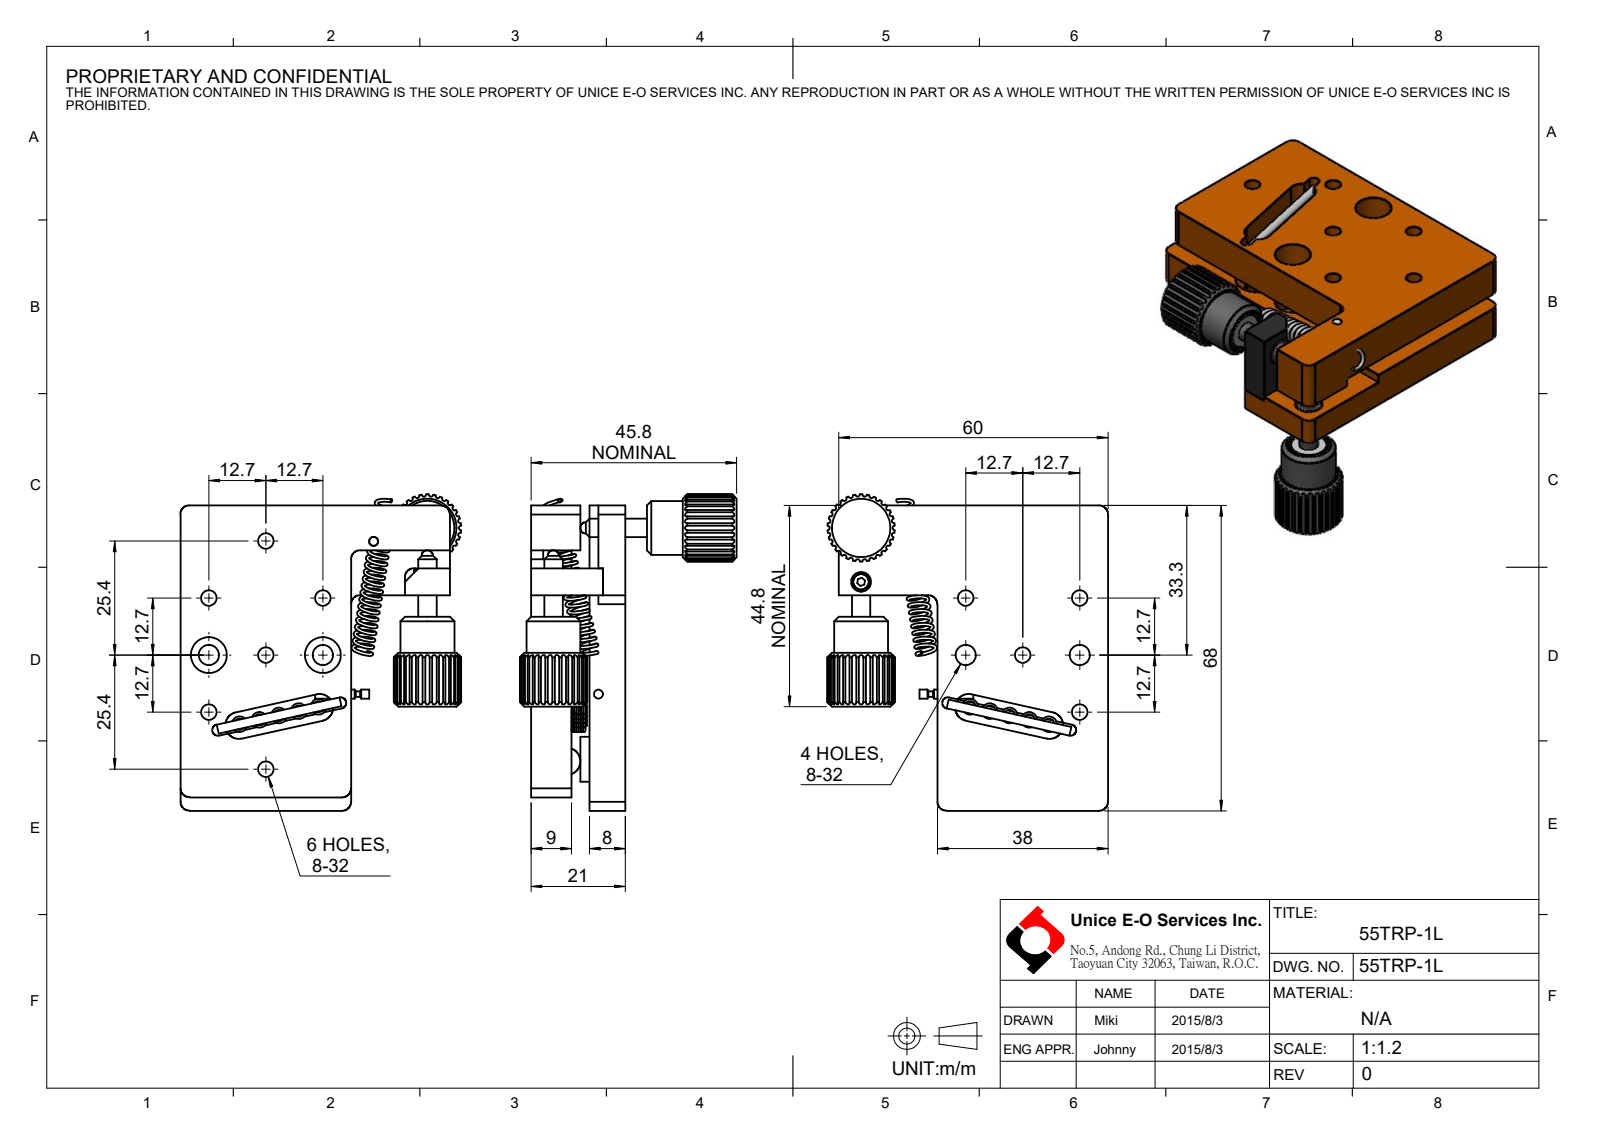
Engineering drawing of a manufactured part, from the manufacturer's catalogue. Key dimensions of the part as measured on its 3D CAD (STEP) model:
Part name (STEP PRODUCT): 55TRP-1L
STEP written by: SolidWorks 2016 (CONFIG_CONTROL_DESIGN)
Units: millimetres
Bodies: 25 solids, 519 faces (136 planar, 304 cylindrical, 79 other)
Overall size (bounding box): 70.5 × 62.5 × 48.28
Volume: 49 369 mm³ · Surface area: 26 222 mm²
Round holes (diameter × count): ⌀3.45 ×8, ⌀3.3 ×3, ⌀2 ×2, ⌀4.5 ×2, ⌀6 ×2, ⌀8 ×2, ⌀9 ×2, ⌀1.6 ×1, ⌀2.4 ×1, ⌀4.4 ×1, ⌀5 ×1
Round bosses / shafts (diameter × count): ⌀2 ×3, ⌀12 ×2, ⌀6 ×2, ⌀4.1 ×2, ⌀3.8 ×1, ⌀2.5 ×1, ⌀1.2 ×1
Partial cylindrical surfaces — rounded edges, fillets, slot ends (radius × count): R0.5 ×60, R2 ×9, R0.75 ×8, R1 ×8, R3 ×6, R1.25 ×2, R7.5 ×2
Main face-to-face distances: 12, 8, 4, 21, 9, 13, 6, 2, 38, 10
Hole centre spacings: 28.4, 17.96, 12.7, 25.4, 40.16, 12.37, 14, 3
